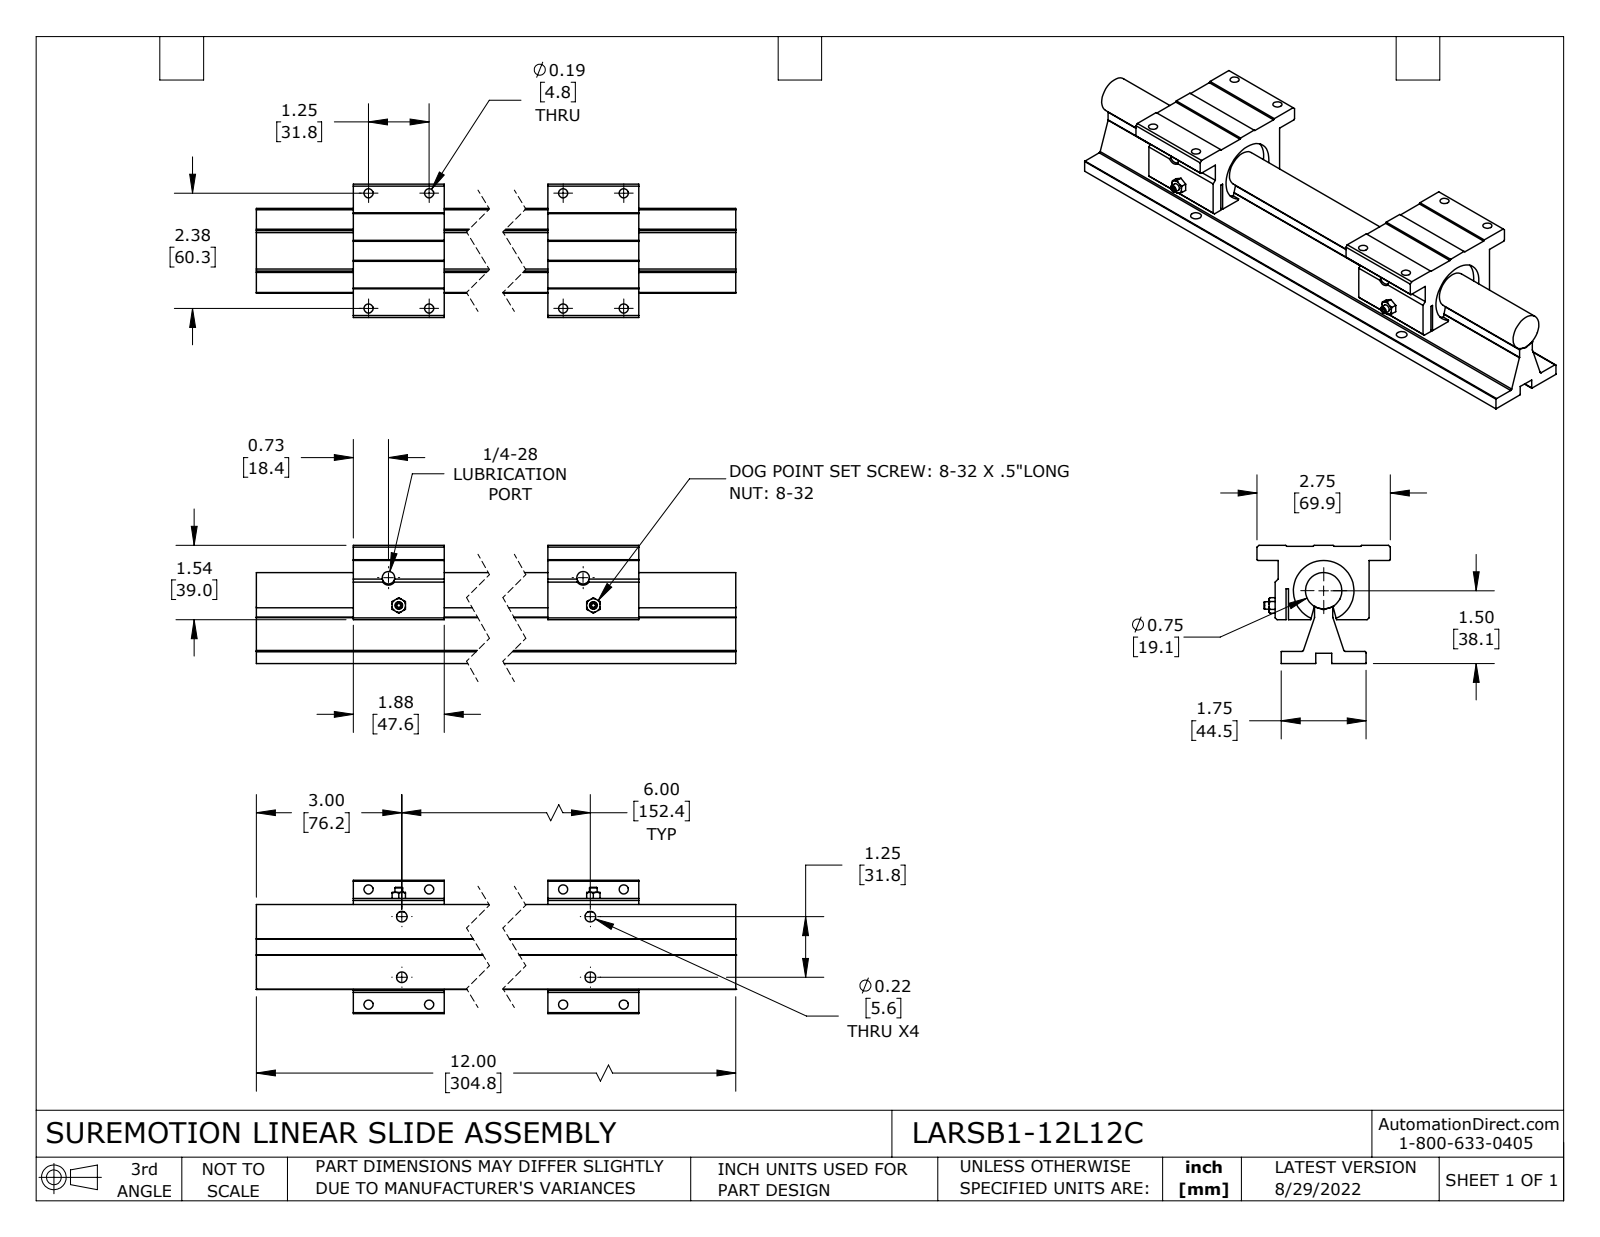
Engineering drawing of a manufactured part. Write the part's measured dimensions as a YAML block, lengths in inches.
part_name: "LARSB1-12L12C; LARSACC-005; LARSB1-12L12C-RAIL"
step_written_by: "SolidWorks 2021 (CONFIG_CONTROL_DESIGN)"
units: inches
bodies: {solids: 4, faces: 211, planar: 125, cylindrical: 66, other: 20}
overall_size: [12, 2.75, 2.437]
volume: 24.92
surface_area: 158.5
round_holes:
  - {diameter: 0.188, count: 8}
  - {diameter: 0.221, count: 4}
  - {diameter: 0.258, count: 2}
  - {diameter: 0.75, count: 1}
  - {diameter: 1.25, count: 1}
round_bosses_or_shafts:
  - {diameter: 0.157, count: 2}
partial_cylinders:
  - {radius: 0.03, count: 11}
  - {radius: 0.06, count: 1}
  - {radius: 0.374, count: 1}
face_to_face_distances: [0.25, 2.437, 2.187, 6.125, 0.71, 1.04, 0.902, 0.652, 1.535, 0.687]
hole_center_spacings: [1.25, 6.125, 2.376, 2.684, 5.467, 5.731, 6.569, 6.711]
